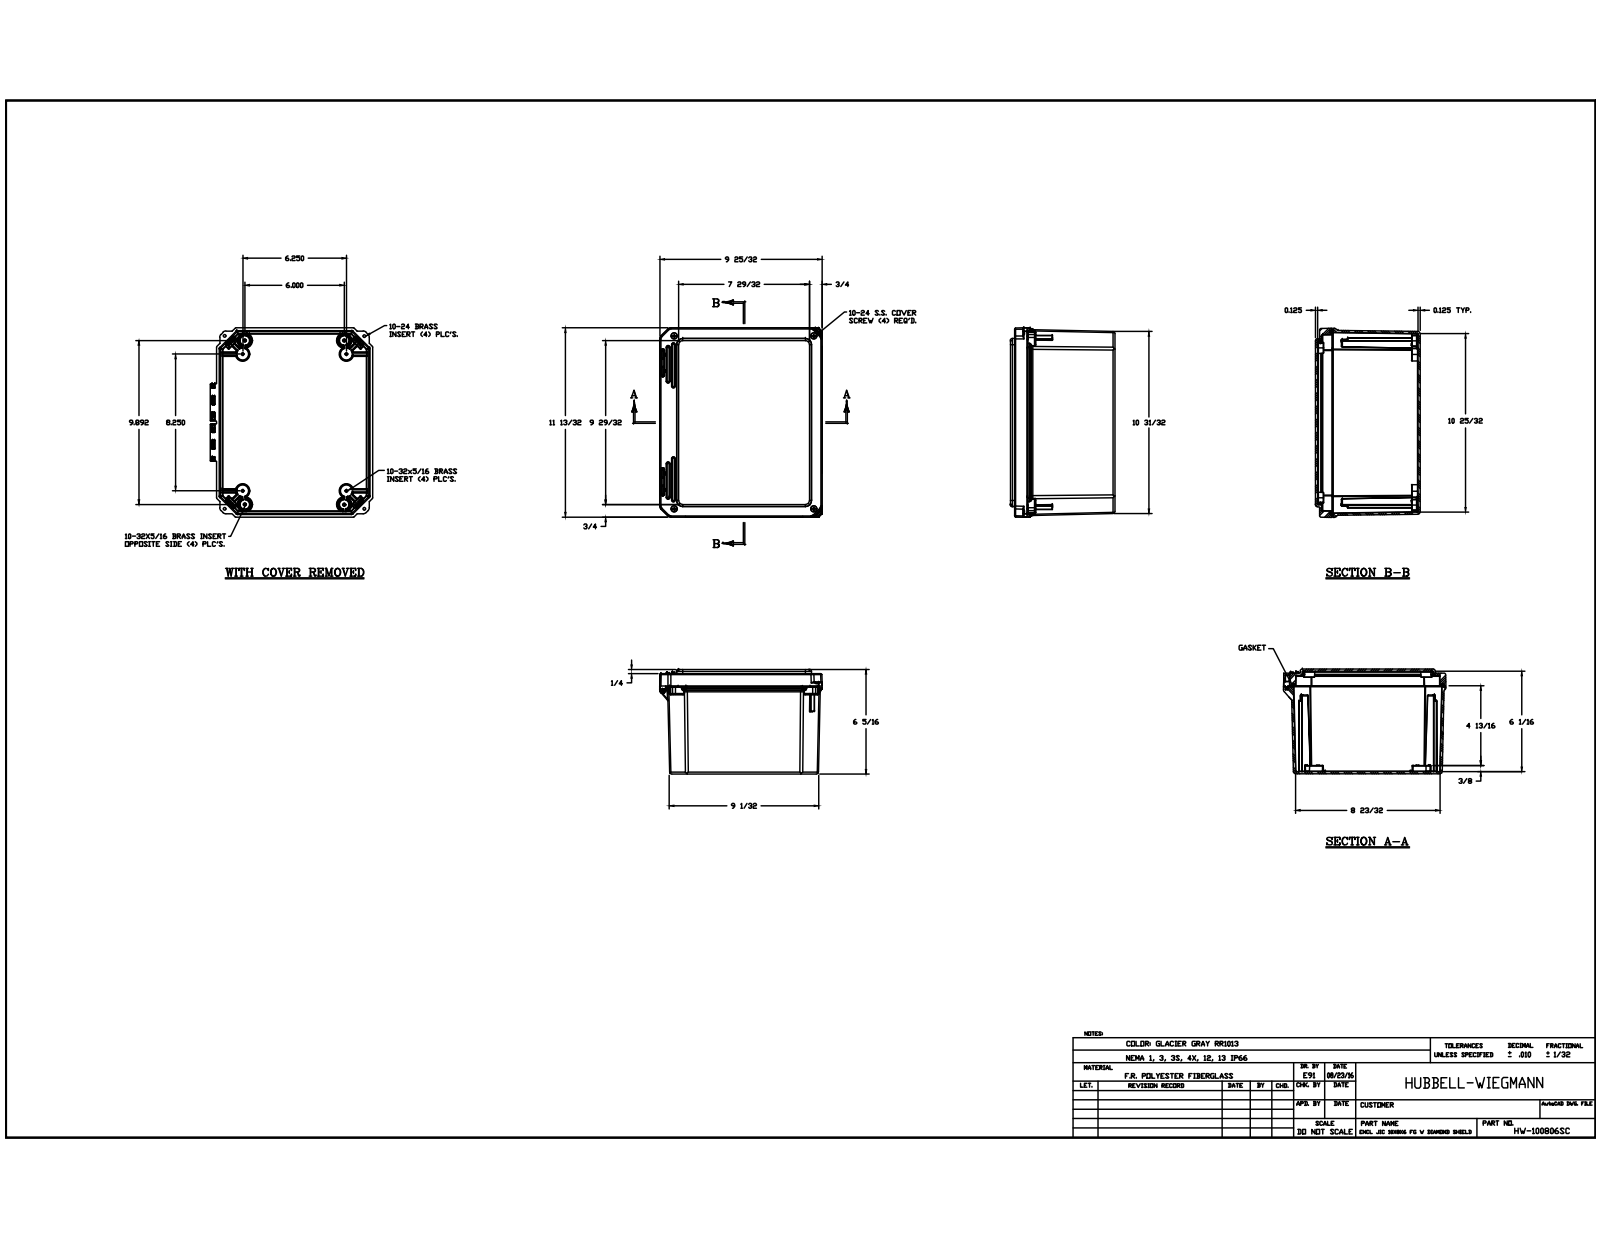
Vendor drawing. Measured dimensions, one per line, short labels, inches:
name: HW-100806SC; DS100806BOX; BRASS INSERT-(; BRASS INSERT-(_1 (+6 more)
written by: Autodesk Inventor 2017 (CONFIG_CONTROL_DESIGN)
unit: in
bodies: 23 solids, 2053 faces (665 planar, 750 cylindrical, 638 other)
size: 11.429 × 9.8 × 6.31
volume: 70.3 in³; area: 979.9 in²
holes: 12× ⌀0.156, 8× ⌀0.152, 4× ⌀0.252, 4× ⌀0.253, 2× ⌀0.219, 2× ⌀0.227, 2× ⌀0.313, 1× ⌀0.137
bosses: 12× ⌀0.246, 4× ⌀0.87, 4× ⌀0.45, 4× ⌀0.199, 2× ⌀0.435
rounds: 157× R0.01, 80× R0.005, 57× R0.02, 44× R0.03, 26× R0.063, 24× R0.03, 24× R0.09, 23× R0.096
face distances: 0.125, 6.185, 0.127, 0.126, 6.31, 6.061, 0.25, 5.935, 0.125, 6.06
hole spacings: 0.831, 6.18, 7.416, 9.072, 9.399, 11.873, 7.216, 10.35
